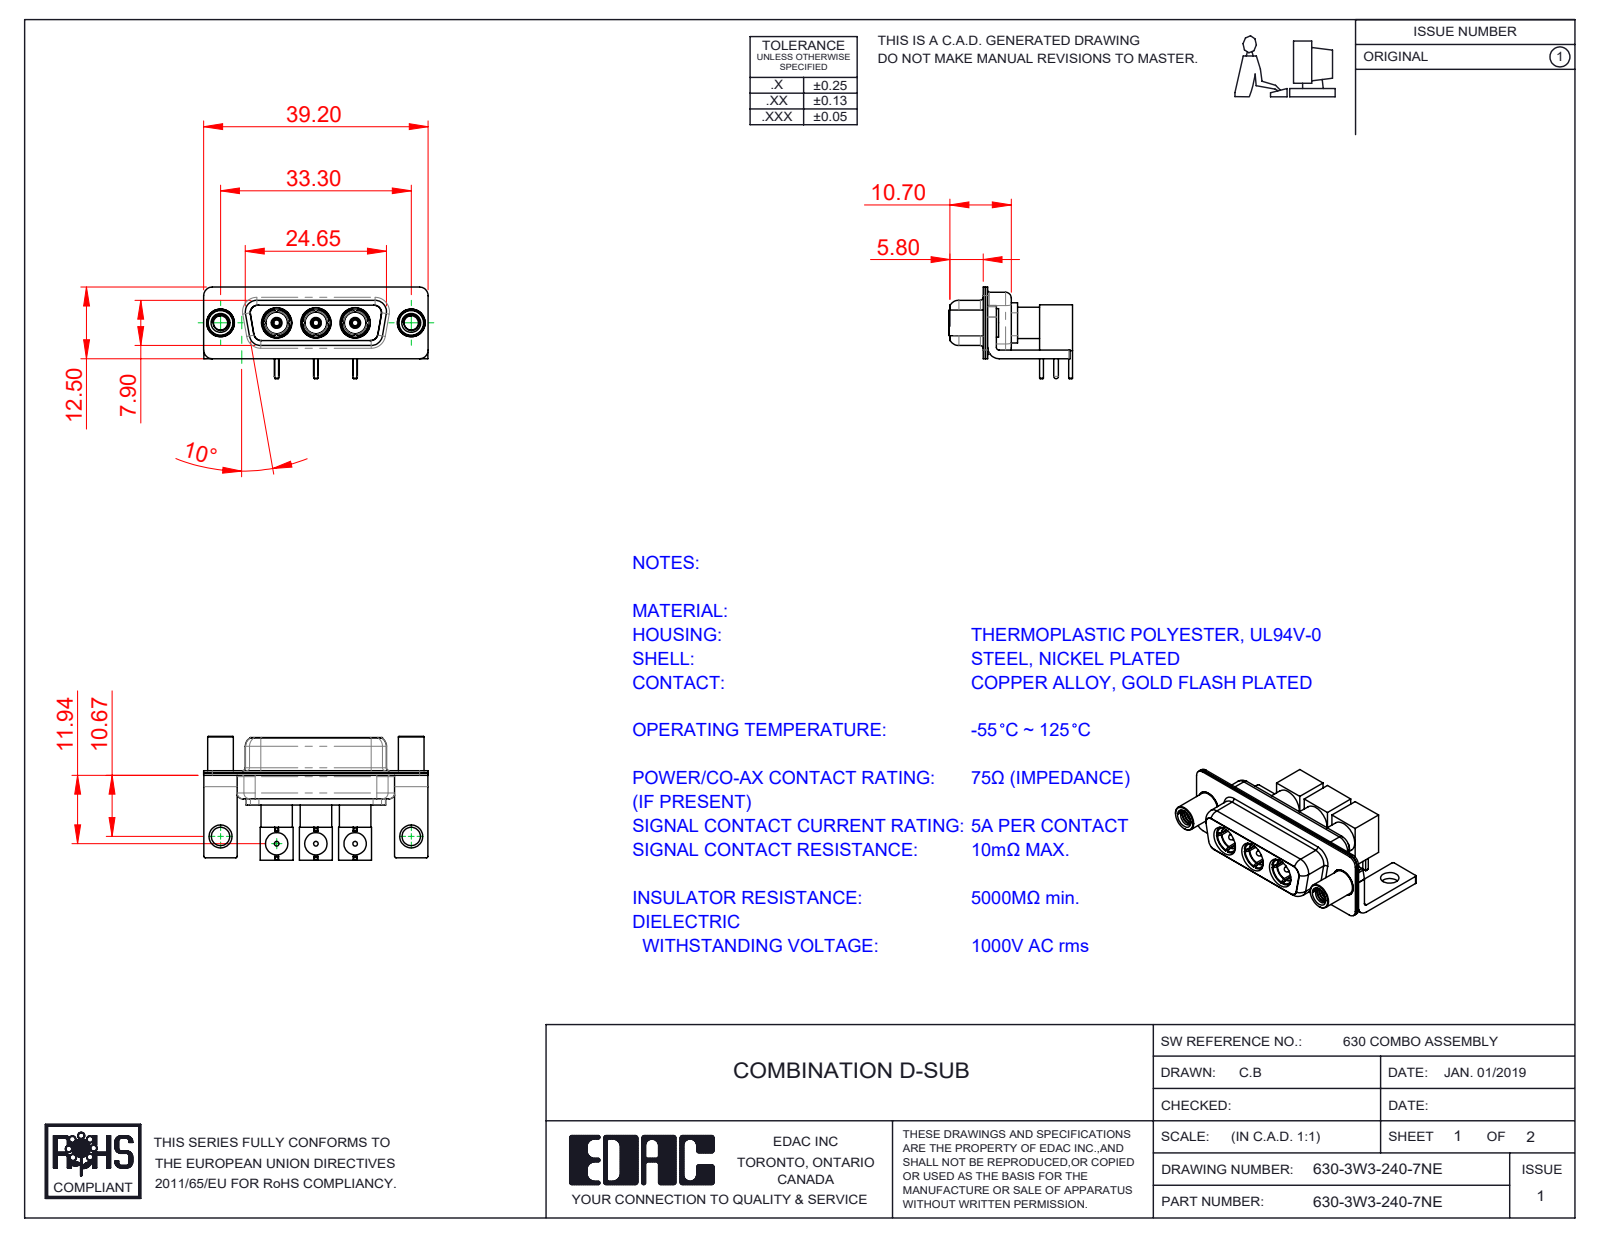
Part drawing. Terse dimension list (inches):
name: Co-Ax Plug Assy_RA; 630Combo Shell Front_15 Contacts; Locking Collar; Insulator Pin_Straight PC Tail (+8 more)
written by: SolidWorks 2020 (CONFIG_CONTROL_DESIGN)
unit: in
bodies: 25 solids, 881 faces (290 planar, 404 cylindrical, 187 other)
size: 1.543 × 0.851 × 0.63
volume: 0.215 in³; area: 13.51 in²
holes: 5× ⌀0.191, 3× ⌀0.031, 3× ⌀0.043, 3× ⌀0.059, 3× ⌀0.111, 3× ⌀0.122, 3× ⌀0.13, 3× ⌀0.154, 3× ⌀0.154, 3× ⌀0.161, 3× ⌀0.209, 2× ⌀0.098
bosses: 5× ⌀0.197, 3× ⌀0.217, 3× ⌀0.205, 3× ⌀0.187, 3× ⌀0.163, 3× ⌀0.157, 3× ⌀0.148, 3× ⌀0.148
rounds: 16× R0.01, 16× R0.059, 13× R0.079, 12× R0.053, 8× R0.063, 5× R0.02, 4× R0.024, 4× R0.026
face distances: 0.016, 0.055, 0.031, 0.071, 0.018, 0.333, 0.35, 0.073, 0.059, 0.244
hole spacings: 0.27, 0.386, 0.389, 0.539, 0.656, 0.657, 0.925, 0.926
